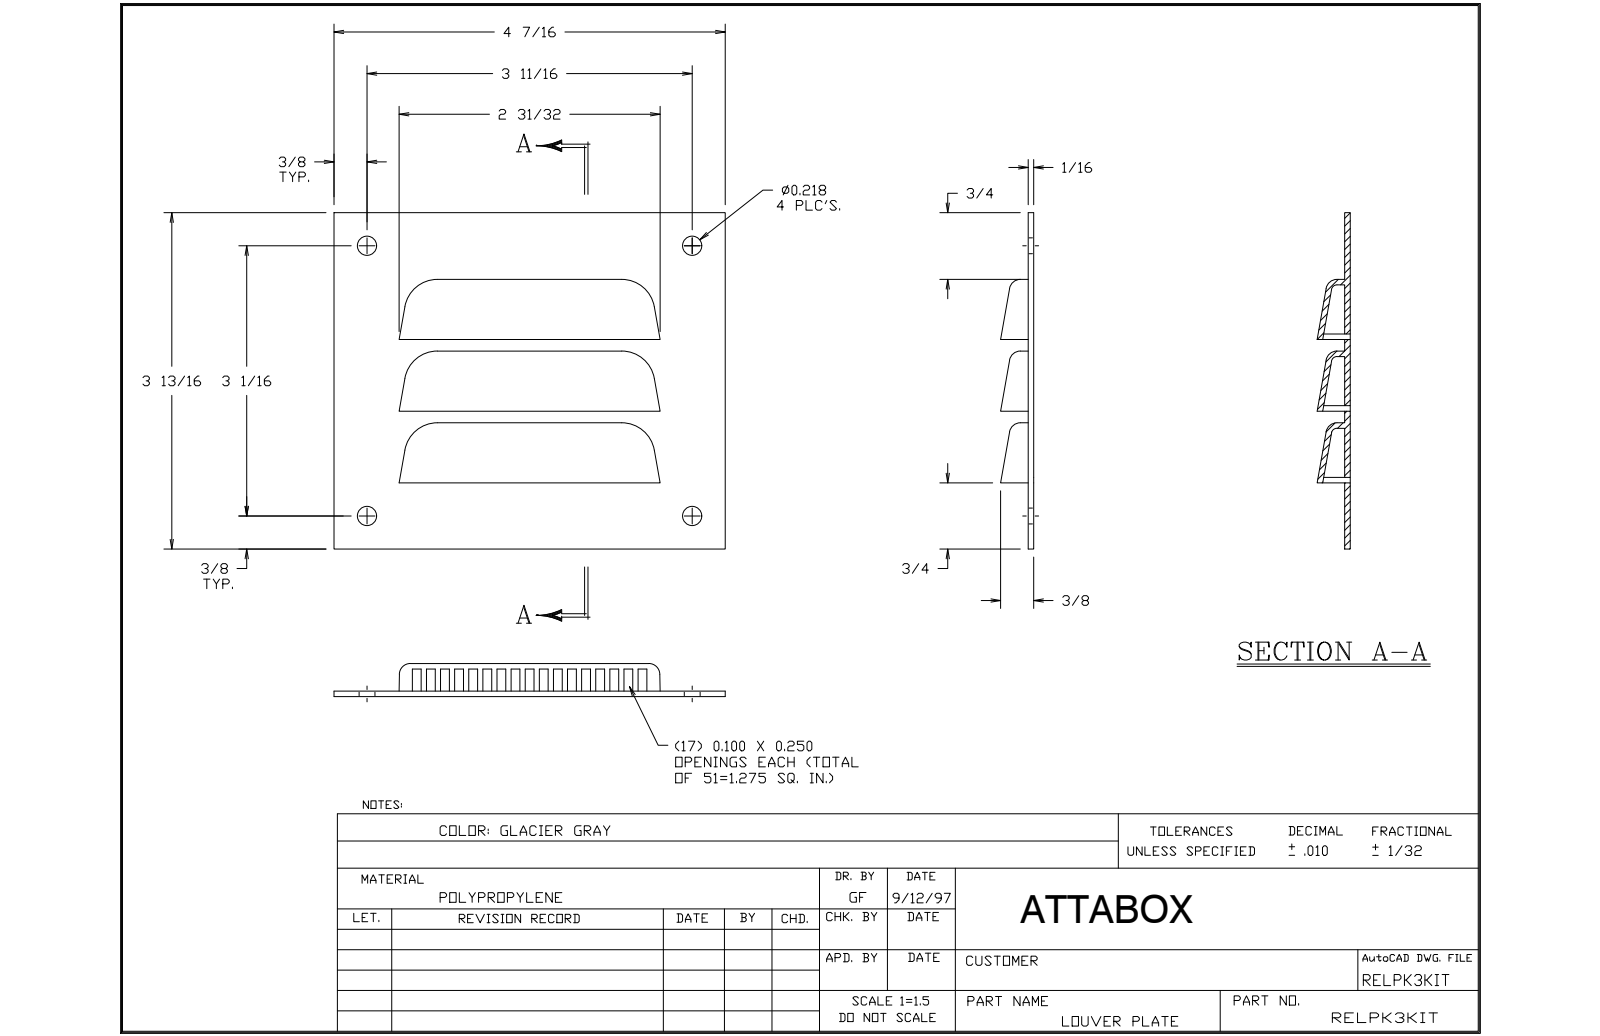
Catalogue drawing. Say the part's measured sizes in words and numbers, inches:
The part is named "RELPK3KIT". Its 3-D file was written by "SolidWorks 2018 (AUTOMOTIVE_DESIGN)". It is 5 solids with 314 faces: 252 planar, 46 cylindrical and 16 other. Overall it measures 4.437 by 3.813 by 0.738 inches. Its volume is 1.306 cubic inches and its surface area 46.59 square inches. Round holes: 4 of diameter 0.1, 4 of diameter 0.218. Round bosses or shafts: 4 of diameter 0.357, 4 of diameter 0.187. Partial cylindrical surfaces (rounded edges, fillets, slot ends): 9 of radius 0.1, 6 of radius 0.038, 6 of radius 0.187, 6 of radius 0.25, 3 of radius 0.037. The main face-to-face distances are 0.063, 0.144, 0.85, 0.289, 0.082, 0.207, 0.591, 1.7, 0.226, 0.352. The hole center spacings are 3.062, 3.687, 4.793.
